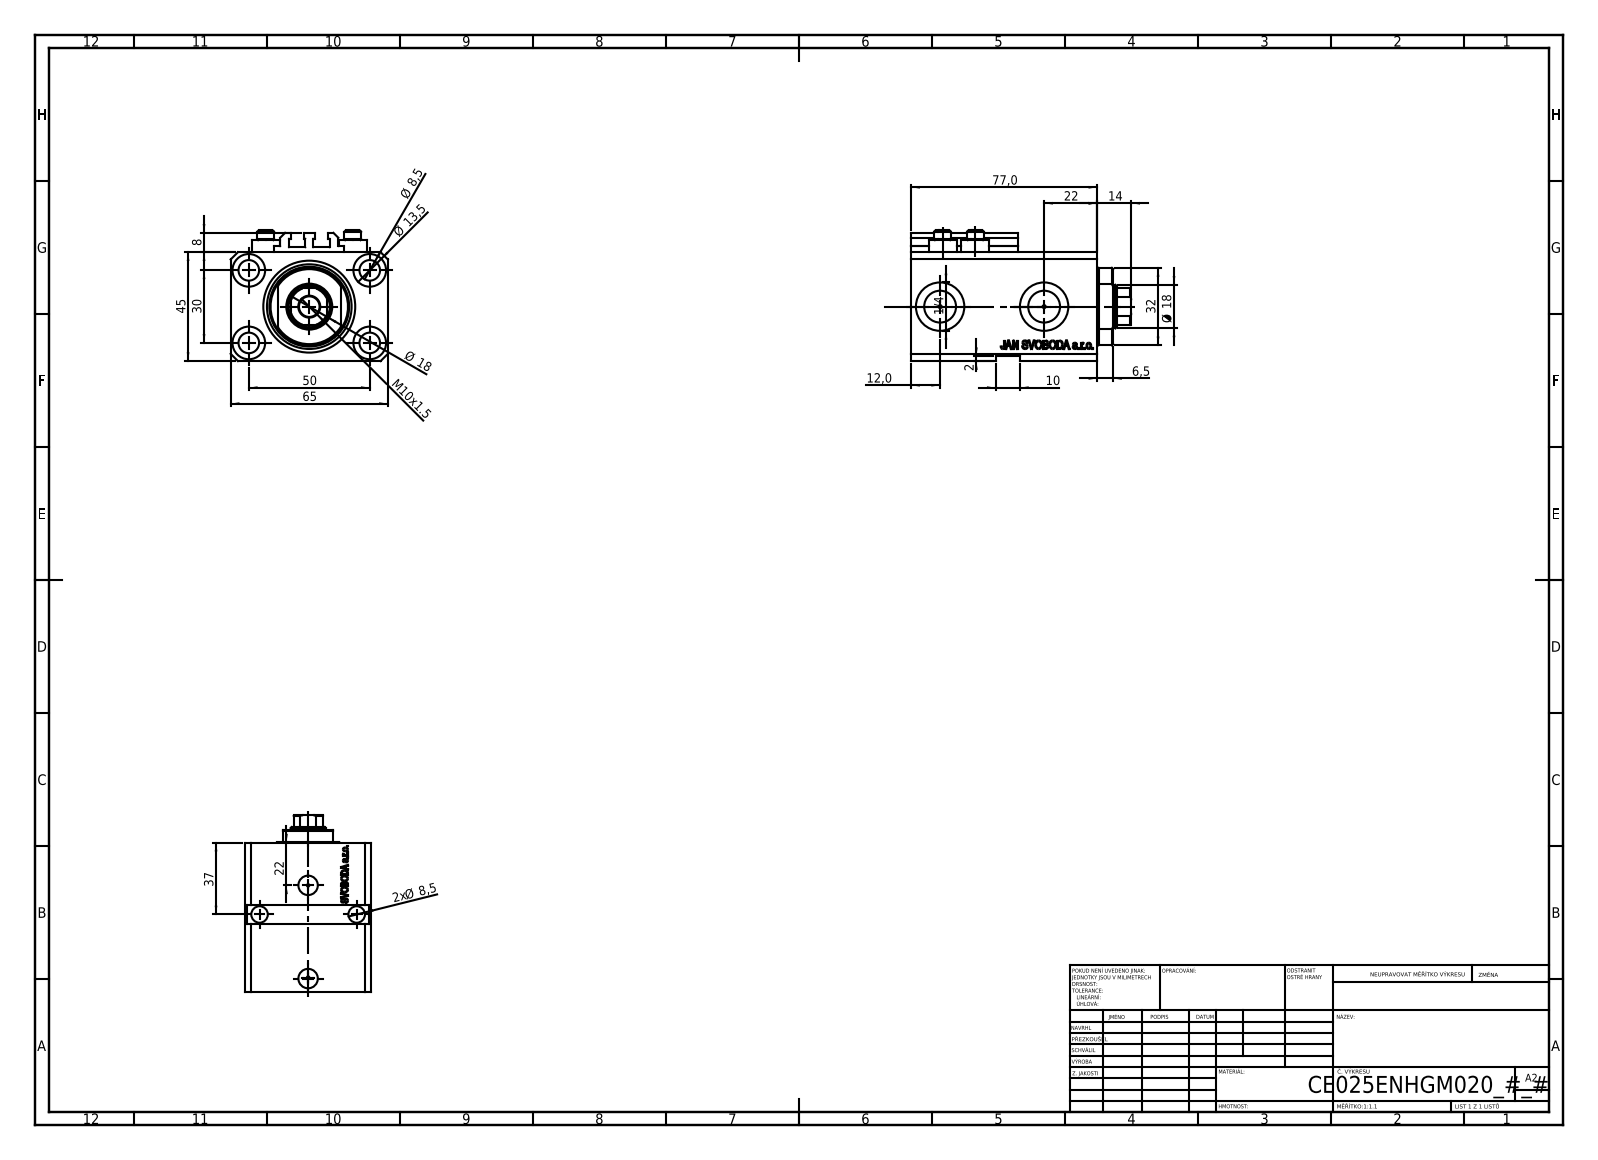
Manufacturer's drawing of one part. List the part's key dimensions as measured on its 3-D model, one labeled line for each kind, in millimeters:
Part name (STEP PRODUCT): V250CE_E_Body; ALLEN BOLT V250CE; V250CE_C_VCP; V250CE_VC_E
STEP written by: SolidWorks 2019 (CONFIG_CONTROL_DESIGN)
Units: millimetres
Bodies: 8 solids, 1067 faces (511 planar, 126 cylindrical, 430 other)
Overall size (bounding box): 91 × 65 × 54
Volume: 199 775 mm³ · Surface area: 59 185 mm²
Round holes (diameter × count): ⌀8.5 ×7, ⌀1.25 ×4, ⌀4 ×4, ⌀13.5 ×4, ⌀10 ×2, ⌀13.16 ×2, ⌀20 ×2, ⌀18 ×1, ⌀25 ×1, ⌀38 ×1
Round bosses / shafts (diameter × count): ⌀11.6 ×4, ⌀7 ×4
Partial cylindrical surfaces — rounded edges, fillets, slot ends (radius × count): R0.2 ×10, R8.5 ×1, R16 ×1
Main face-to-face distances: 45, 65, 63, 14, 77, 2, 6.9, 56.1, 70.1, 47
Hole centre spacings: 29.15, 50, 13.6, 15.12, 18.81, 18.97, 26.22, 26.61
